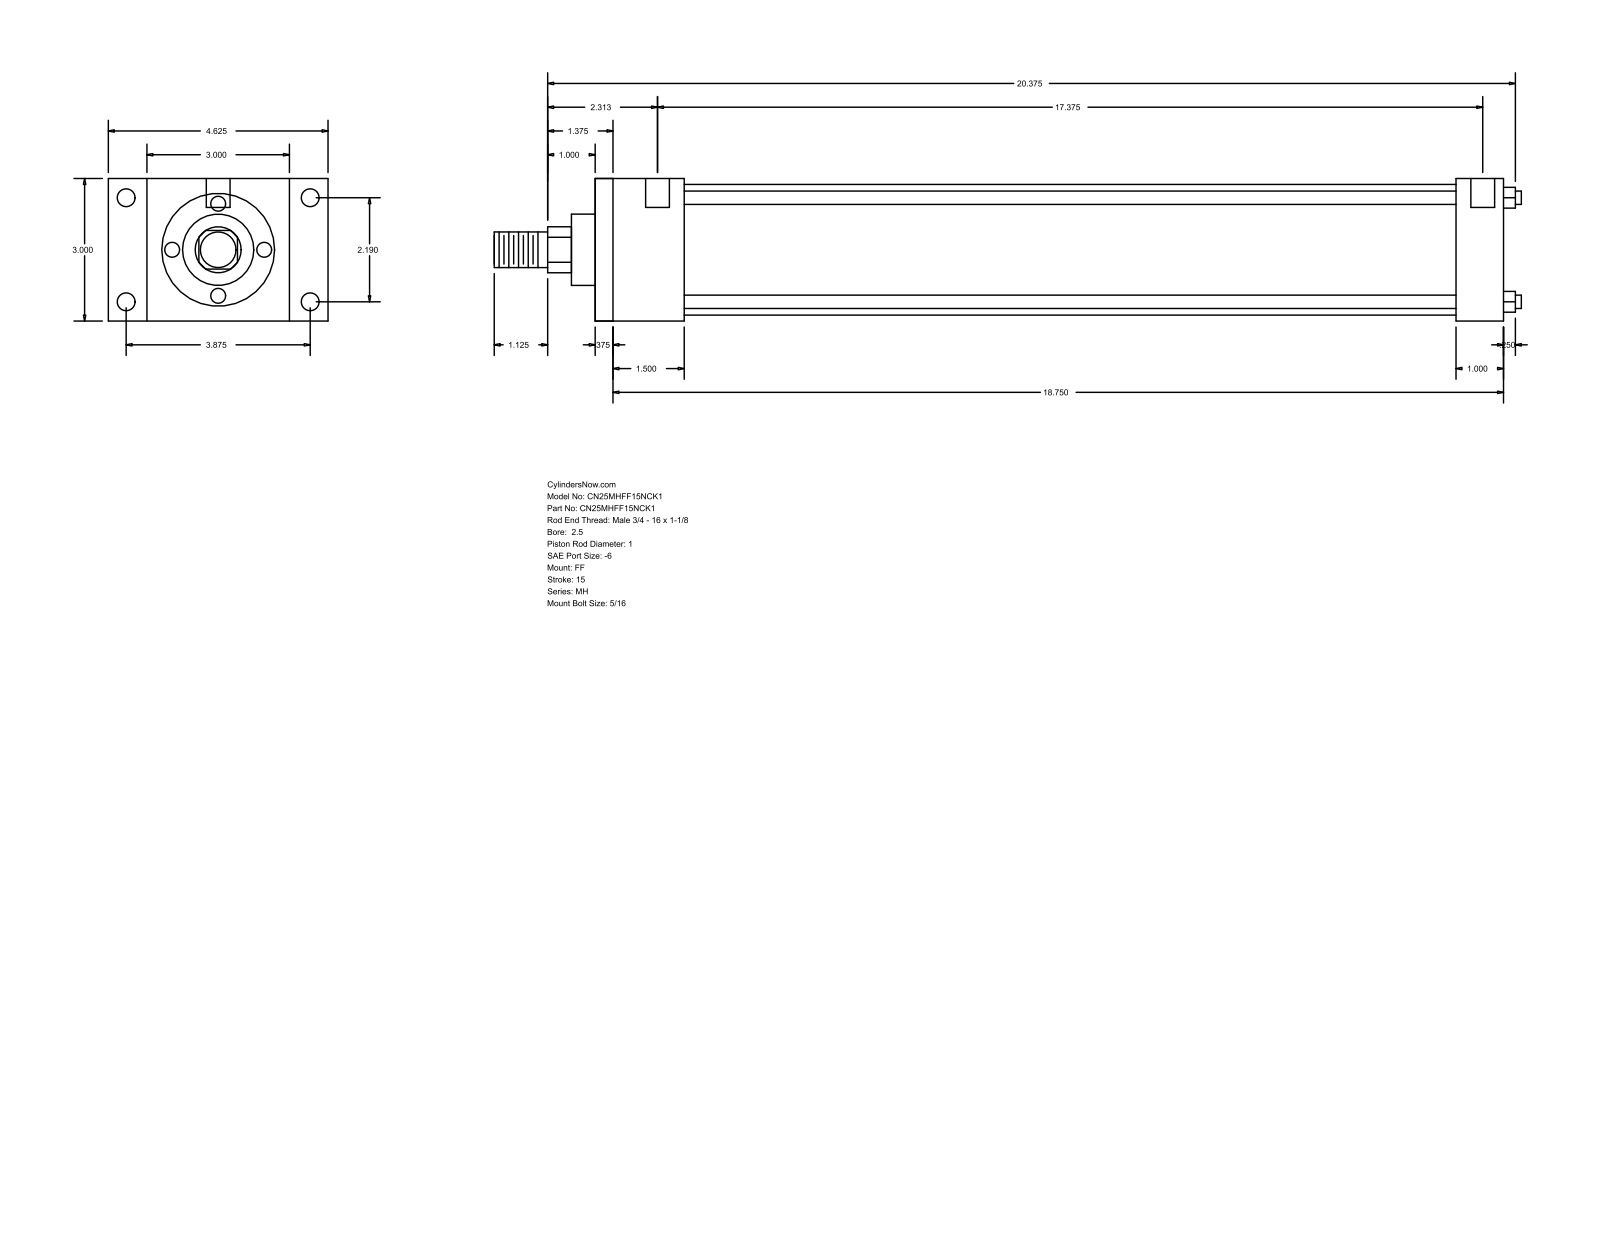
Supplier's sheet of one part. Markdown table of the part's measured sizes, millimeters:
| quantity | value |
| --- | --- |
| part name | MH_FF__0250_1 |
| STEP written by | GSSL Pune (CONFIG_CONTROL_DESIGN) |
| units | millimeters |
| bodies | 0 solids, 92 faces (64 planar, 28 cylindrical, 0 other) |
| overall size | 549.27 × 117.47 × 76.2 |
| round holes (diameter × count) | 5.56 × 4, 9.53 × 4, 12.7 × 2 |
| round bosses / shafts (diameter × count) | 7.14 × 4, 69.85 × 1, 38.1 × 1, 25.4 × 1, 19.05 × 1 |
| partial cylindrical surfaces (radius × count) | 12.29 × 1 |
| main face-to-face distances | 76.2, 485.78, 9.52, 476.26, 47.63, 460.37, 38.11, 450.85, 412.74, 438.15 |
| hole center spacings | 55.62, 98.42, 113.05, 449.26, 3.18, 4.76, 441.32, 444.5 |
